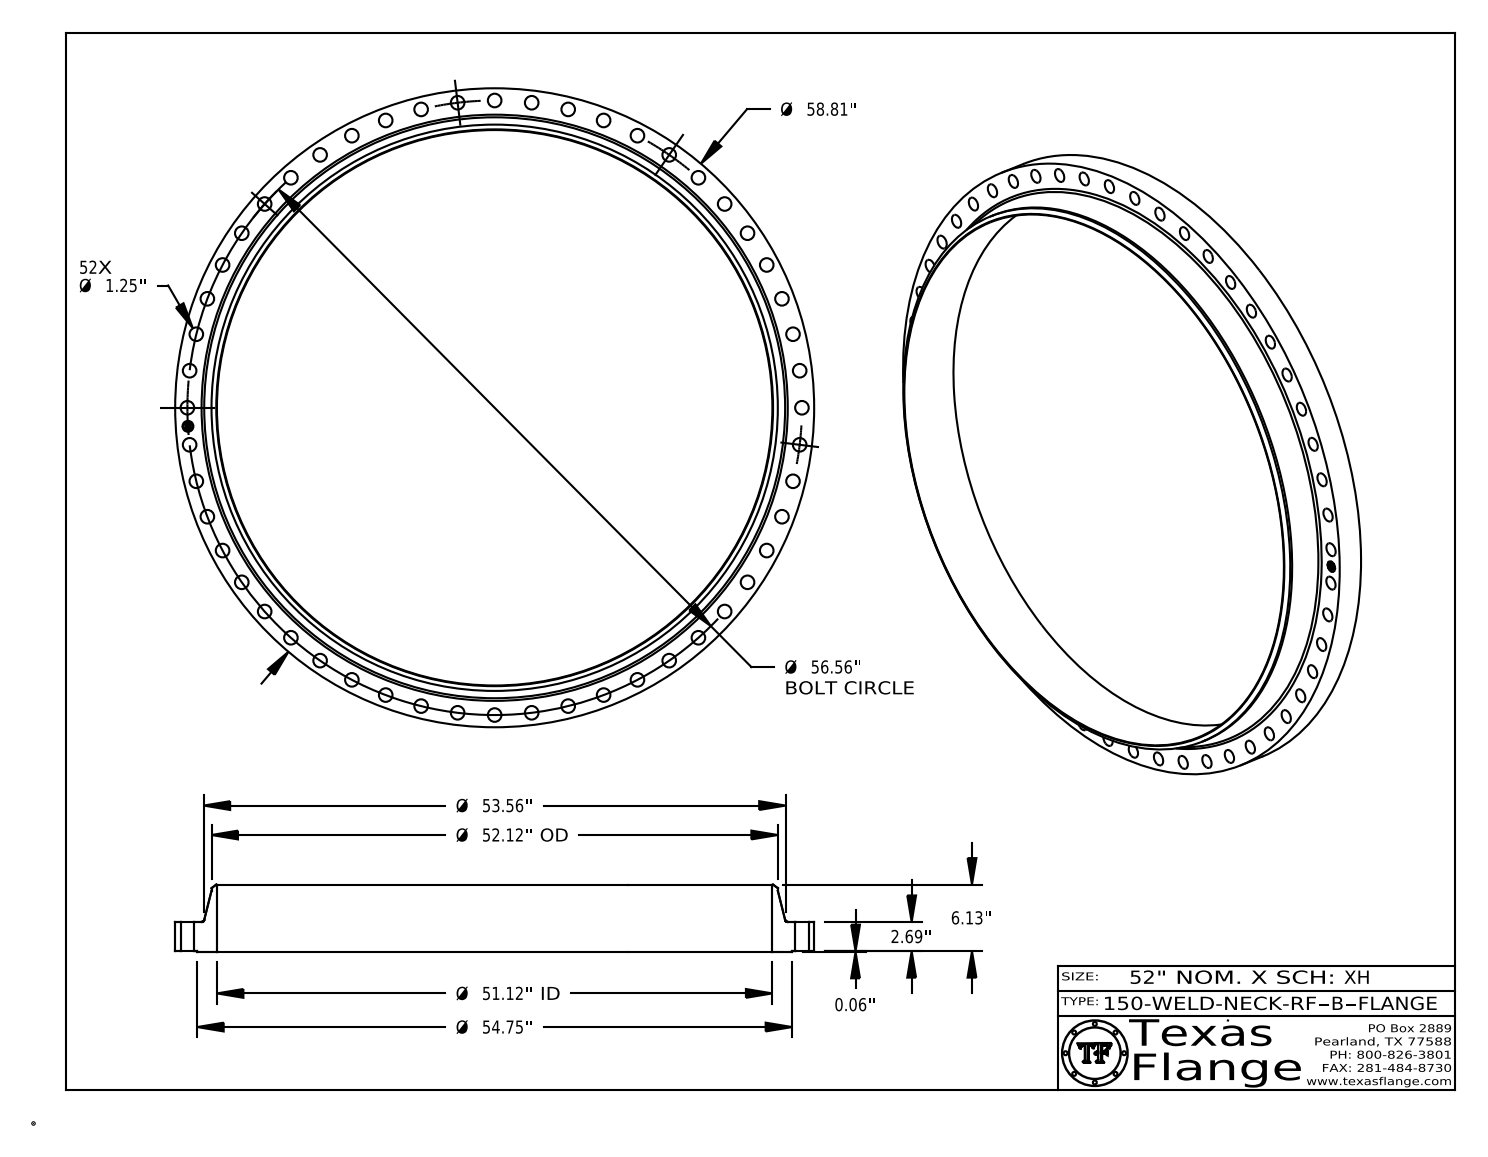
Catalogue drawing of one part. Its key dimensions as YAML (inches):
part_name: "150-WELD-NECK-RF, Series B"
step_written_by: "CATIA V5 STEP AP214 (AUTOMOTIVE_DESIGN)"
units: inches
bodies: {solids: 1, faces: 507, planar: 369, cylindrical: 132, other: 6}
overall_size: [58.81, 58.81, 6.193]
volume: 2072
surface_area: 3671
round_holes:
  - {diameter: 1.25, count: 52}
  - {diameter: 1, count: 1}
  - {diameter: 51.12, count: 1}
round_bosses_or_shafts:
  - {diameter: 0.061, count: 8}
  - {diameter: 58.81, count: 1}
  - {diameter: 54.75, count: 1}
  - {diameter: 52.12, count: 1}
  - {diameter: 0.788, count: 1}
face_to_face_distances: [2.753, 0.063, 2.69, 6.193, 6.13, 3.44, 2.738, 2.675, 0.015, 3.455]
hole_center_spacings: [28.28, 56.457, 3.415, 56.148, 6.817, 55.633, 10.195, 16.827]
